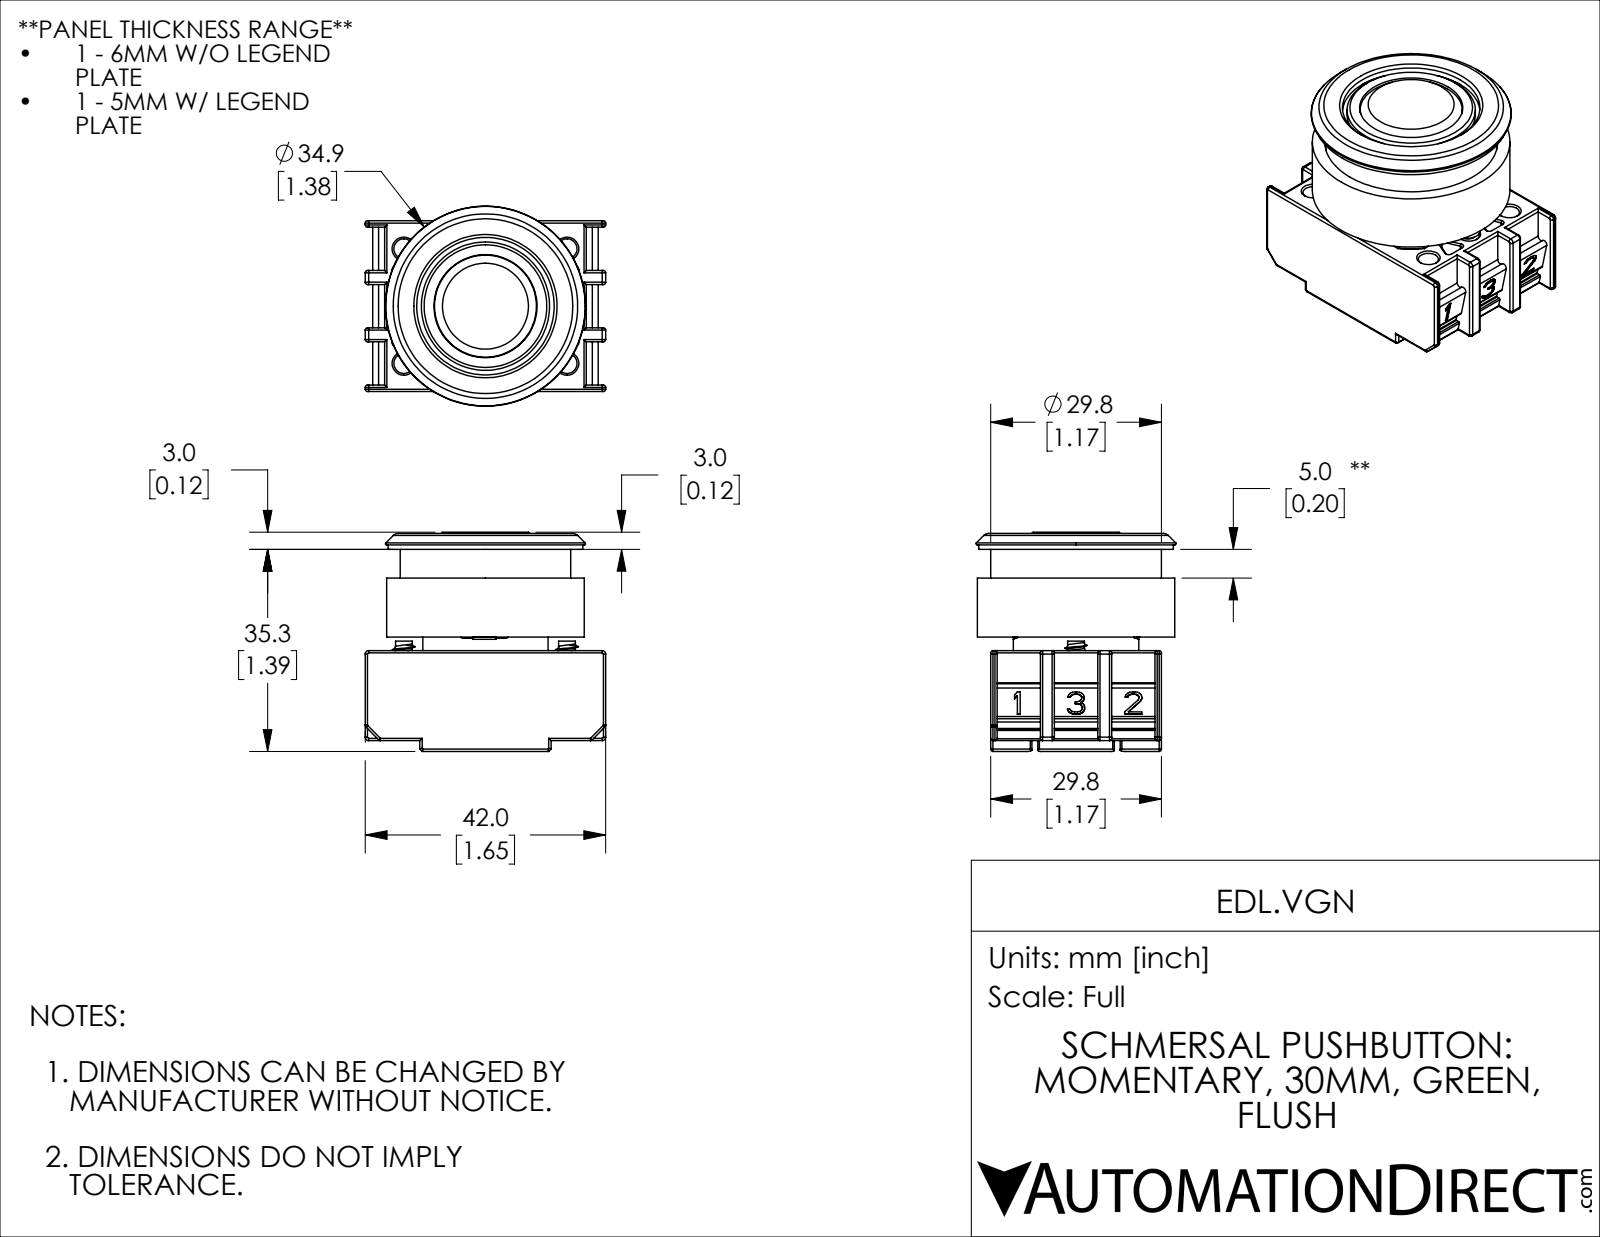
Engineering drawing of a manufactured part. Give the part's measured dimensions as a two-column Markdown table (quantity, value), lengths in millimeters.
| quantity | value |
| --- | --- |
| part name | EDL.VGN |
| STEP written by | SolidWorks 2019 (CONFIG_CONTROL_DESIGN) |
| units | millimeters |
| bodies | 5 solids, 1372 faces (506 planar, 465 cylindrical, 401 other) |
| overall size | 42 × 38.25 × 34.93 |
| volume | 25 195 mm³ |
| surface area | 19 662 mm² |
| round holes (diameter × count) | 3.5 × 6, 5.15 × 6, 10.4 × 1, 13.1 × 1, 18 × 1, 24 × 1, 24.2 × 1, 27 × 1, 30.2 × 1 |
| round bosses / shafts (diameter × count) | 4.8 × 2, 2.93 × 2, 34.5 × 1, 34 × 1, 29.8 × 1, 22.4 × 1, 21.9 × 1, 17.8 × 1 |
| partial cylindrical surfaces (radius × count) | 0.4 × 112, 0.3 × 48, 0.2 × 32, 0.6 × 8, 0.5 × 6, 0.1 × 2, 0.6 × 2, 0.8 × 2 |
| main face-to-face distances | 29.8, 16.1, 19.95, 2.35, 10, 5, 1.9, 18.45, 10.3, 15.7 |
| hole center spacings | 10, 17.41, 30.2, 28.5, 14.25, 20, 34.82 |
